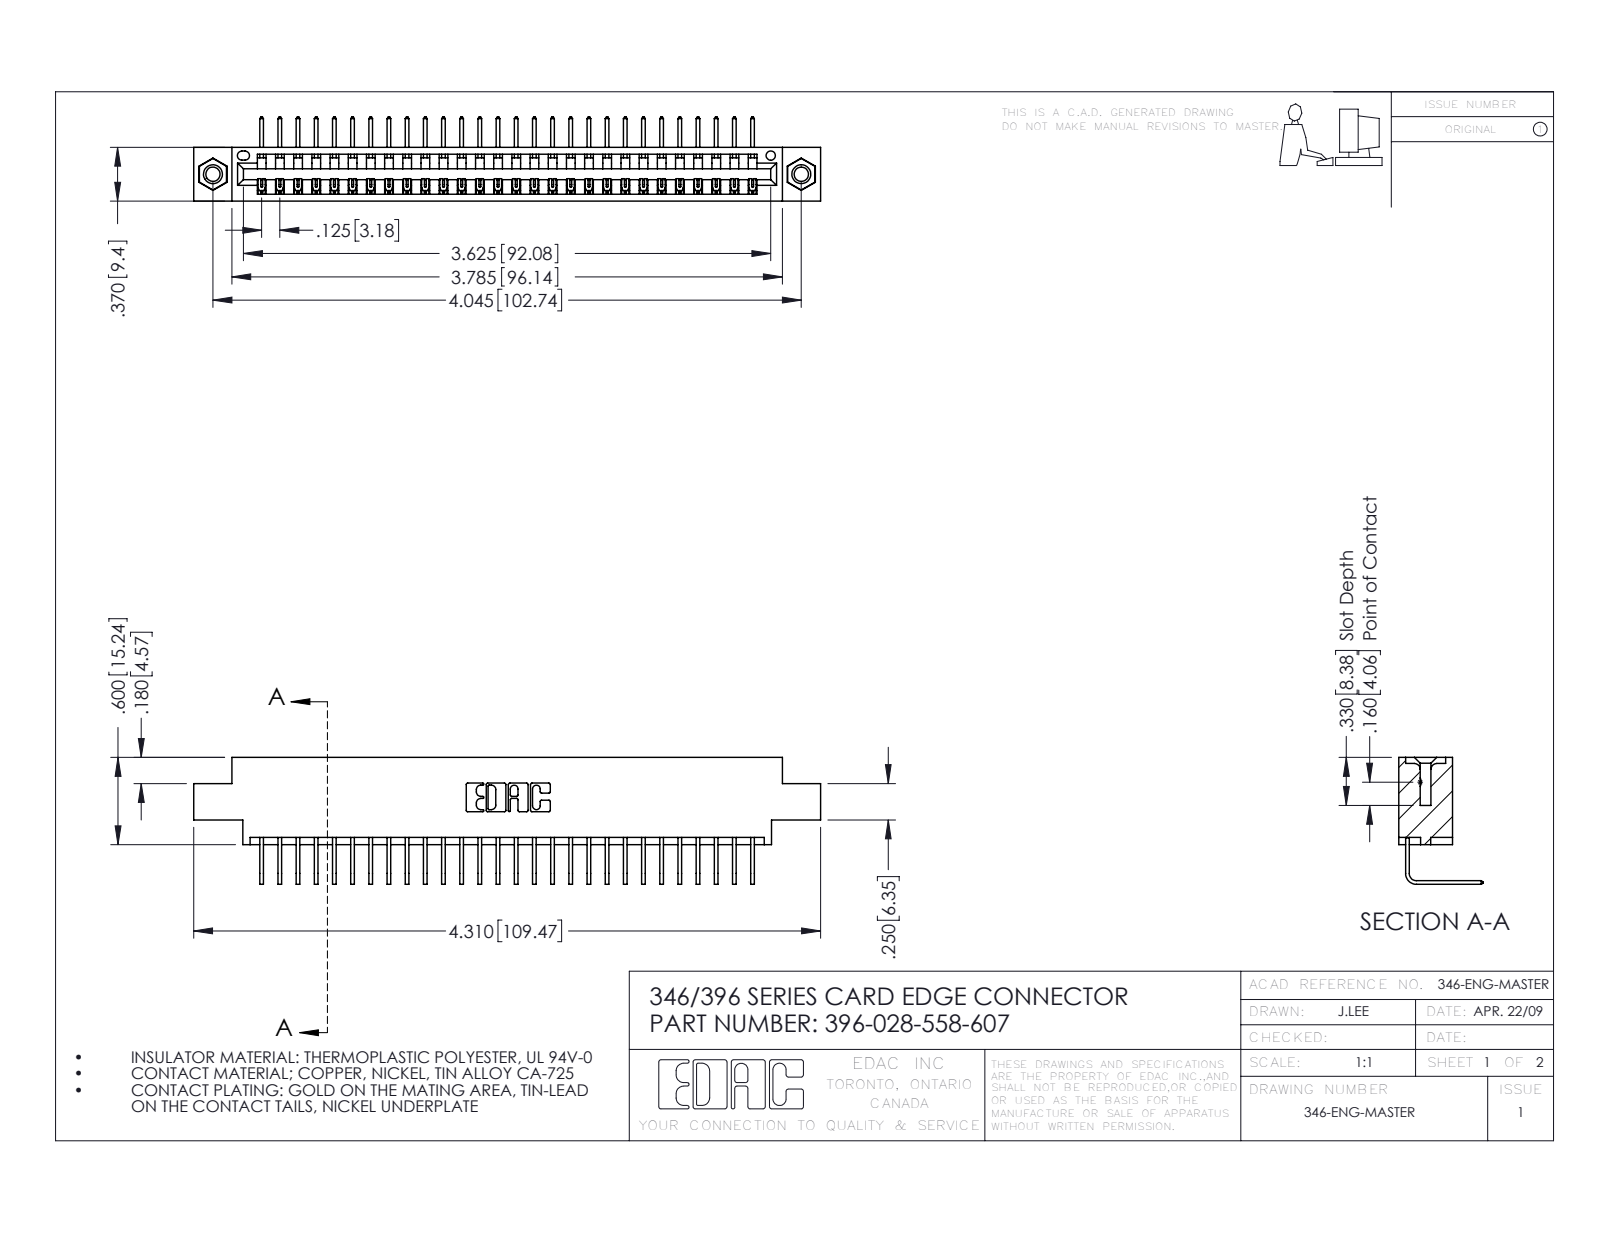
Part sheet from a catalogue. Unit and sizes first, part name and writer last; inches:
Units: inches
Overall size (bounding box): 4.31 × 0.873 × 0.58
Round holes (diameter × count): ⌀0.098 ×2, ⌀0.125 ×2, ⌀0.156 ×2, ⌀0.064 ×1
Round bosses / shafts (diameter × count): ⌀0.155 ×2
Partial cylindrical surfaces — rounded edges, fillets, slot ends (radius × count): R0.006 ×56, R0.01 ×22, R0.007 ×6, R0.031 ×6, R0.026 ×3, R0.031 ×2, R0.04 ×2, R0.014 ×1
Main face-to-face distances: 0.322, 0.048, 0.37, 0.25, 0.298, 0.025, 0.072, 0.222, 0.148, 0.1
Hole centre spacings: 0.246, 3.837, 4.045
Volume: 0.629 in³ · Surface area: 20.9 in²
Bodies: 31 solids, 1866 faces (1288 planar, 562 cylindrical, 16 other)
Part name (STEP PRODUCT): 396-028-558-607; 345-250-001_345-250-005-103; 346 Part_0.170 Offset - 0.156 Dia-TI; 345-292-001_558 Tail - 2
STEP written by: SolidWorks 2016 (CONFIG_CONTROL_DESIGN)
